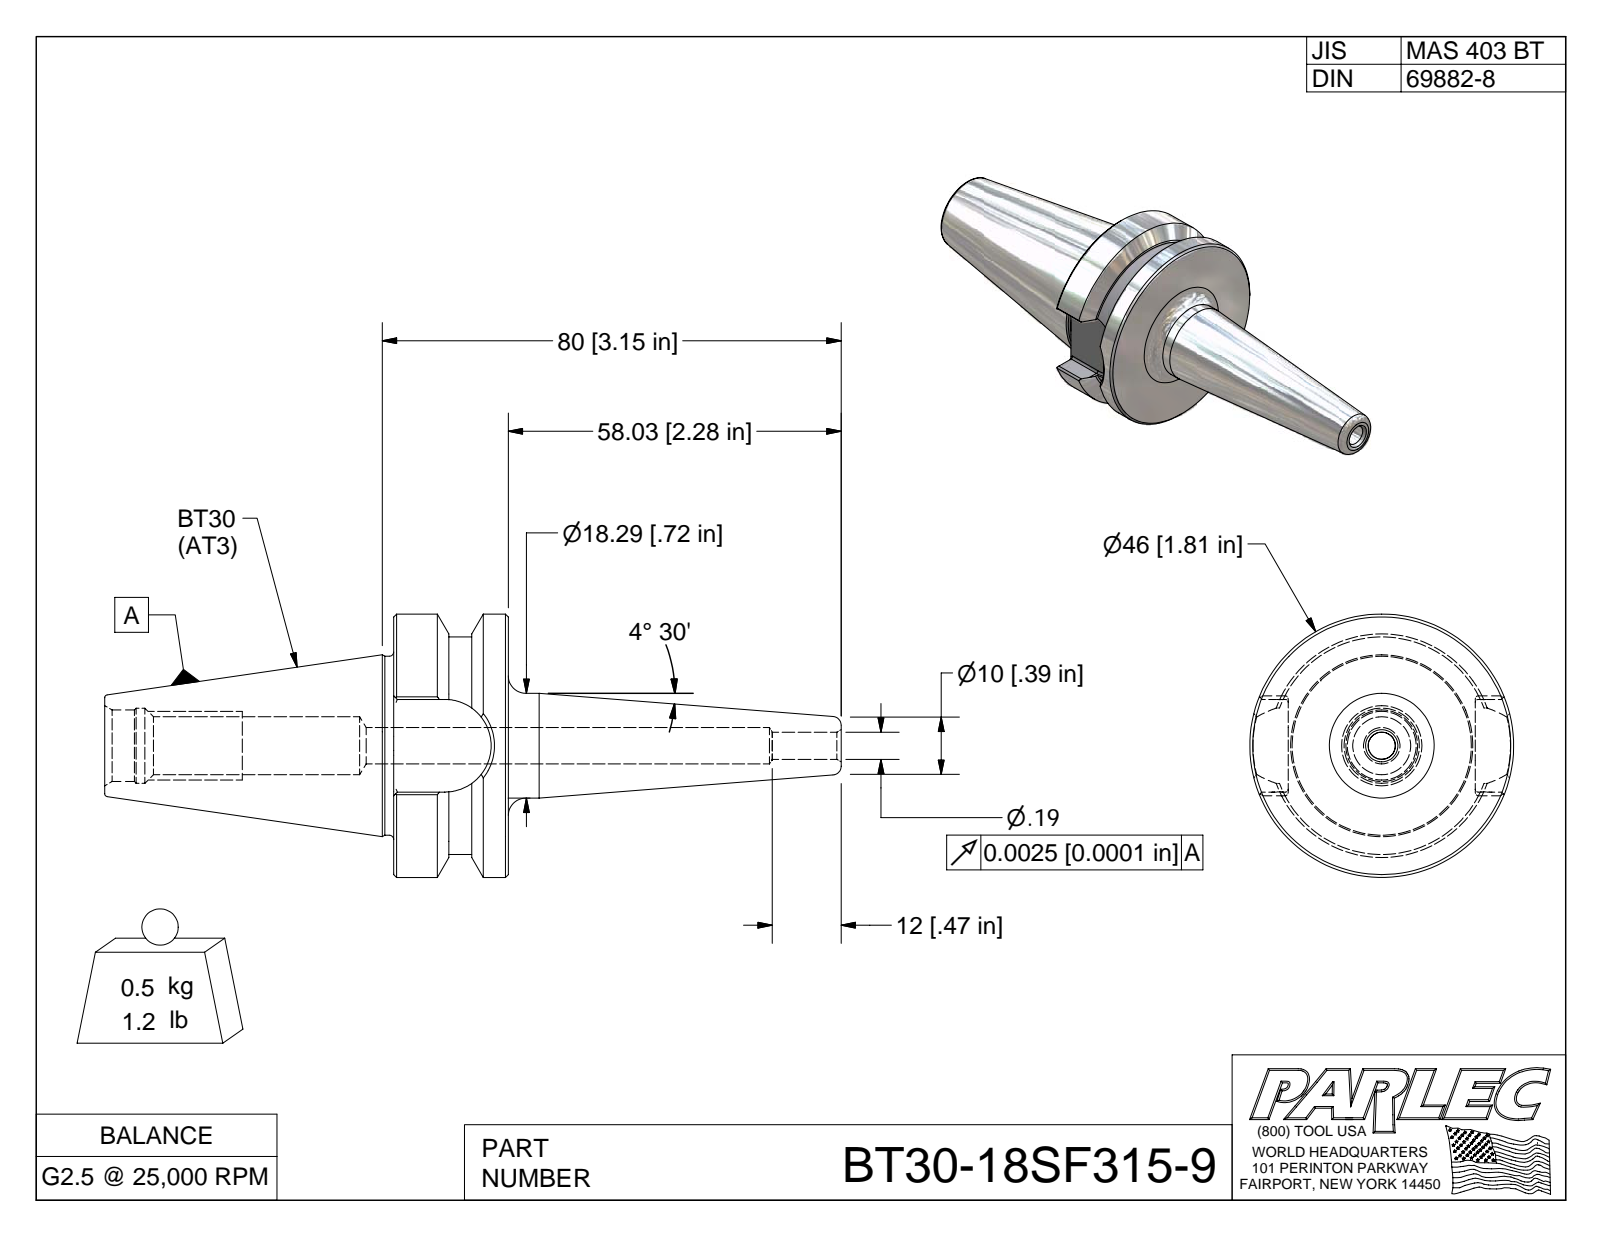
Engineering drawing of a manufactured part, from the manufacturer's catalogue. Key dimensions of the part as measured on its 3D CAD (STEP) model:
Part name (STEP PRODUCT): BT30-18SF315-9; BT30-18SF315-9-1
STEP written by: Autodesk Inventor 2009 (AUTOMOTIVE_DESIGN)
Units: inches
Bodies: 1 solid, 70 faces (23 planar, 19 cylindrical, 28 other)
Overall size (bounding box): 5.056 × 1.811 × 1.811
Volume: 3.456 in³ · Surface area: 23.93 in²
Round holes (diameter × count): ⌀0.187 ×1, ⌀0.517 ×1
Round bosses / shafts (diameter × count): ⌀1.811 ×1, ⌀1.23 ×1, ⌀0.72 ×1
Partial cylindrical surfaces — rounded edges, fillets, slot ends (radius × count): R0.02 ×8, R0.319 ×1, R0.748 ×1
Main face-to-face distances: 0.787, 1.283, 1.984, 2.771, 0.637, 2.52, 0.536, 0.251, 2.363, 0.379
